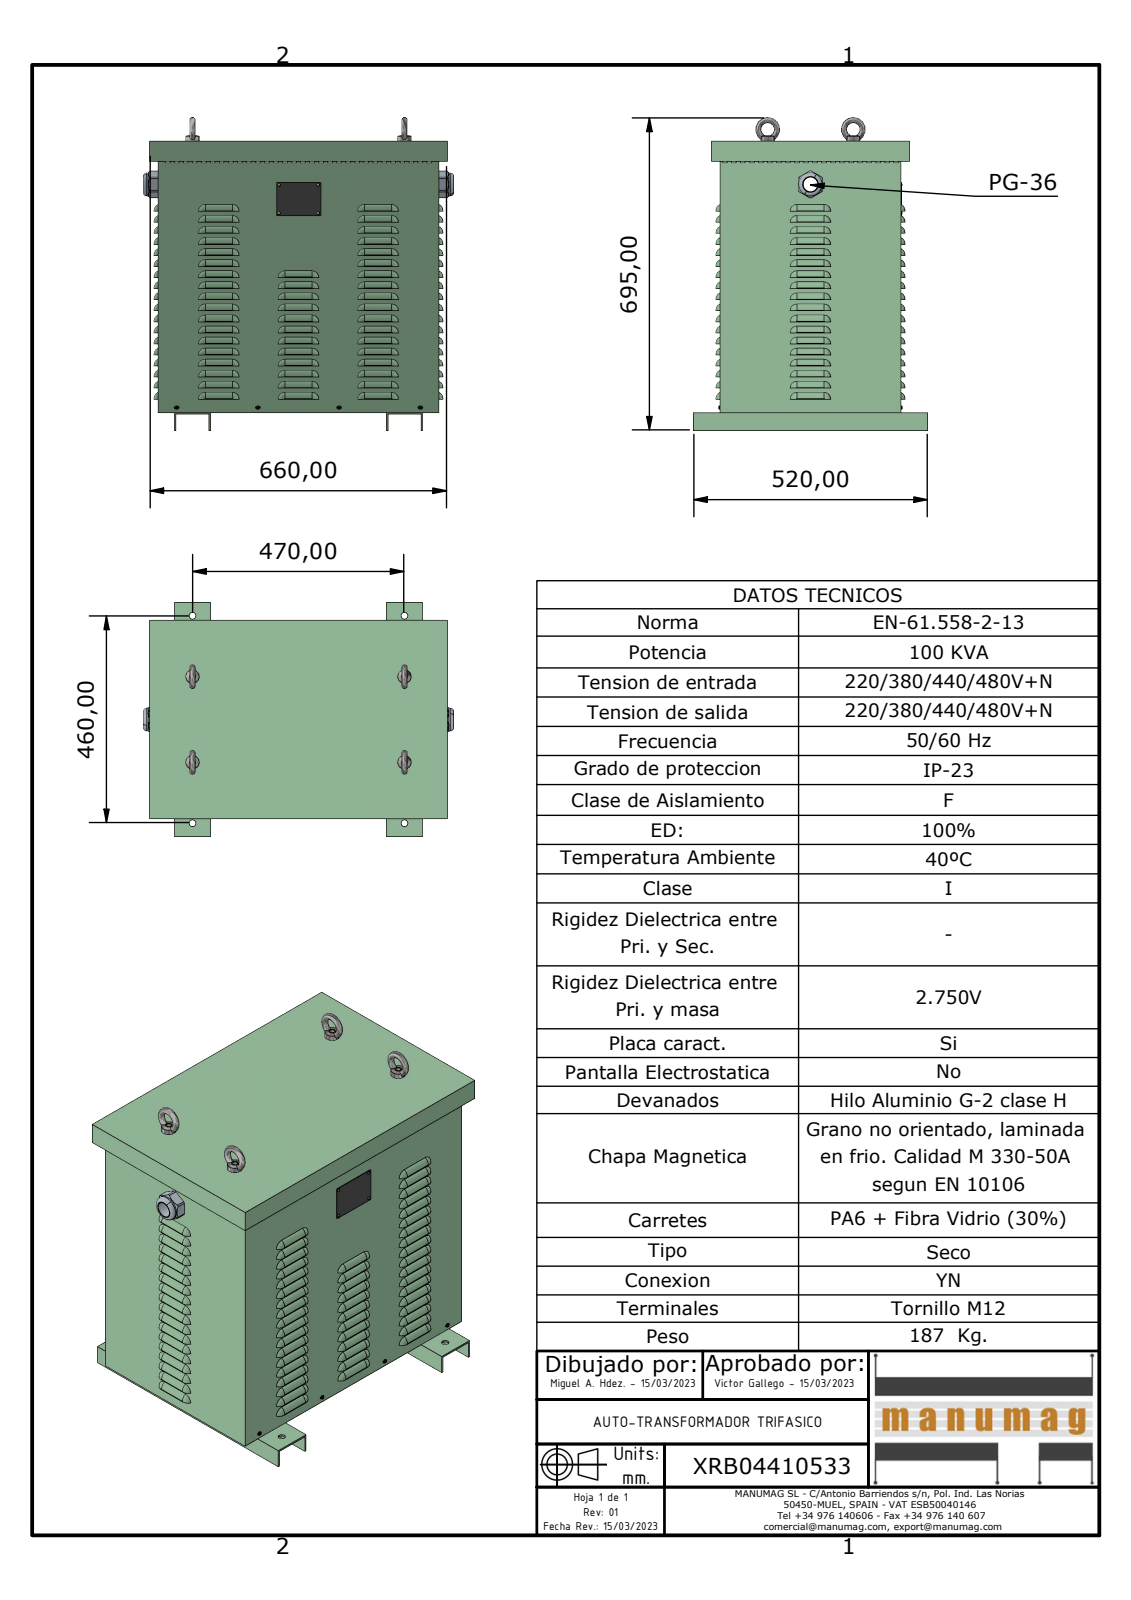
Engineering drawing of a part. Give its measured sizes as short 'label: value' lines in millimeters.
name: XRB04410533; JE100 CUERPO; JE100 BASE; PLACA CARACTERISTICAS (+6 more)
written by: Autodesk Inventor 2023 (AUTOMOTIVE_DESIGN)
unit: mm
bodies: 24 solids, 3065 faces (1141 planar, 1208 cylindrical, 716 other)
size: 695 × 688.2 × 520
volume: 4 880 000 mm³; area: 4 293 000 mm²
holes: 558× ⌀11, 8× ⌀15, 4× ⌀4, 4× ⌀5, 4× ⌀10.11, 1× ⌀32, 1× ⌀48
bosses: 4× ⌀30, 4× ⌀4, 4× ⌀3.62, 4× ⌀3.2, 2× ⌀51.1, 1× ⌀47.45, 1× ⌀47
rounds: 132× R14, 72× R7, 72× R15, 12× R3.88, 8× R2.5, 4× R2, 2× R30
face distances: 2, 400, 600, 621, 398, 402, 602, 619, 598, 623
hole spacings: 30, 15, 582, 582.77, 199, 45, 582.19, 583.74
